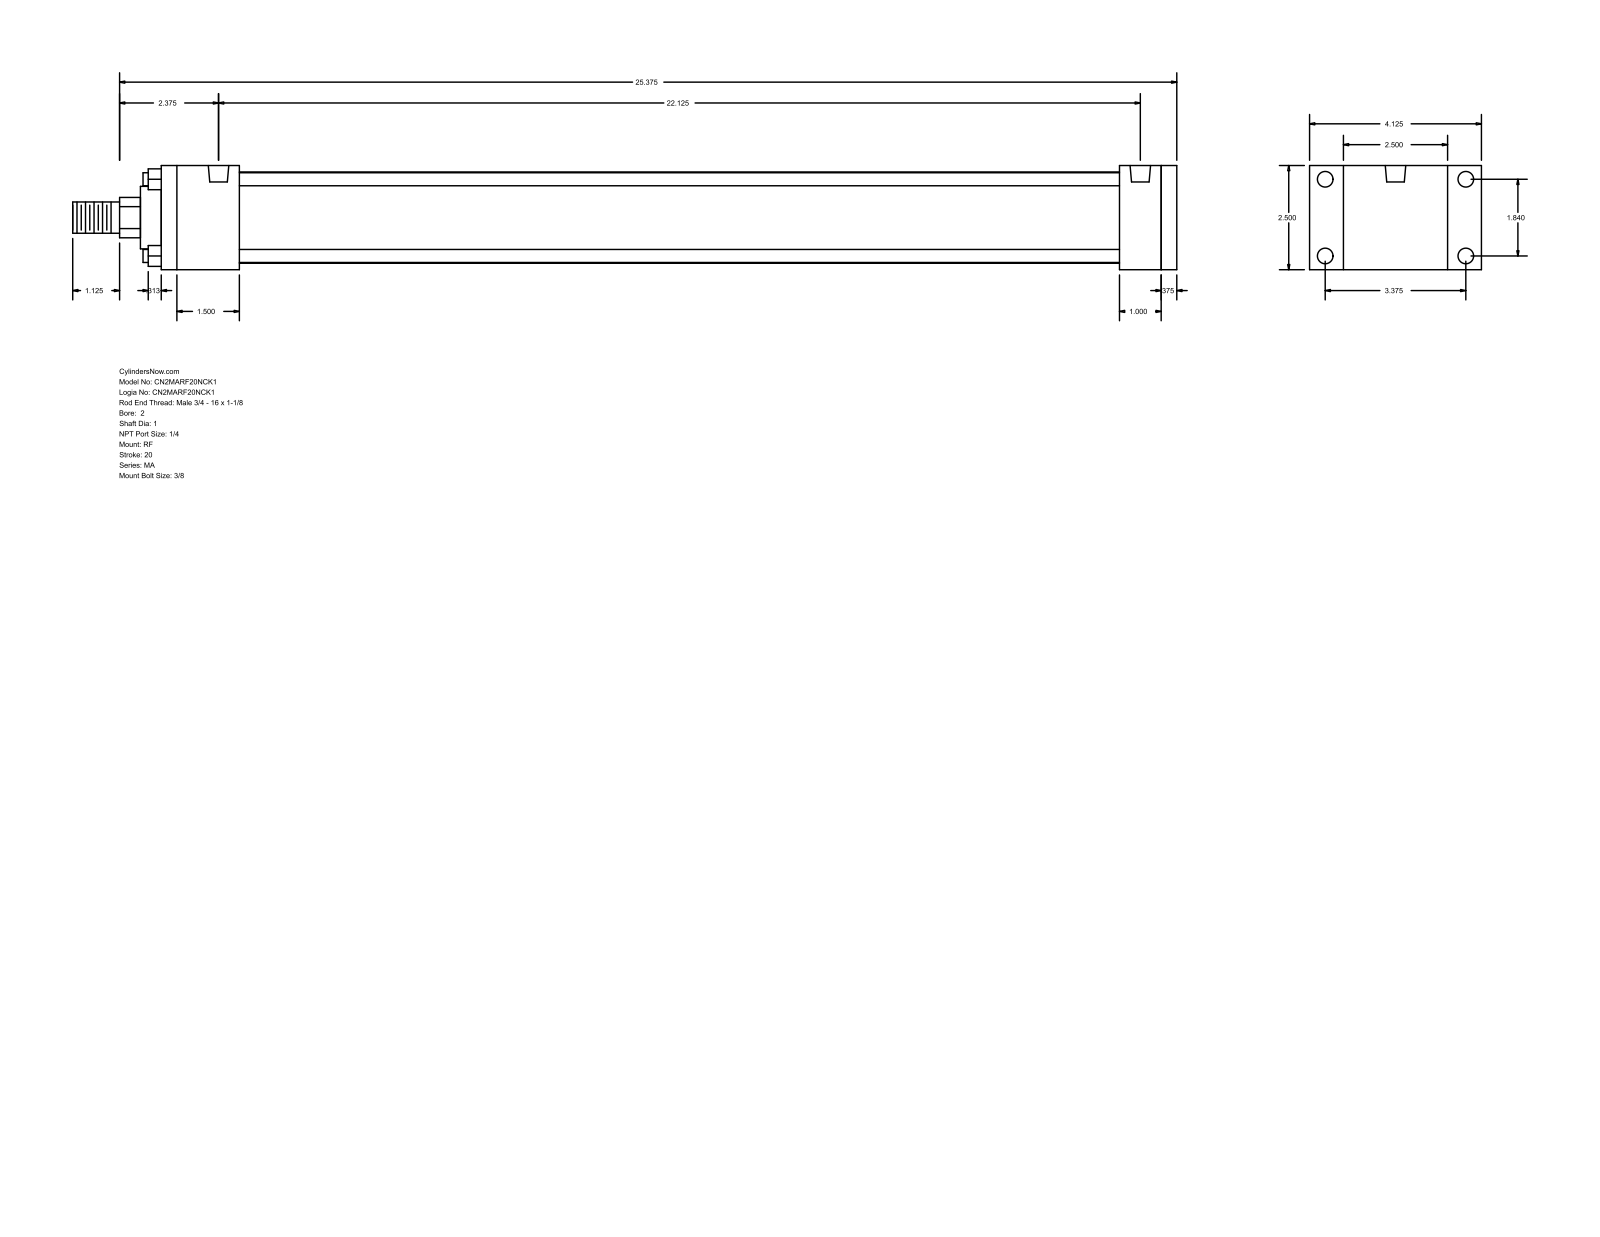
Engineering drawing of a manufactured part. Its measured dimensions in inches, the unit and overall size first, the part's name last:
Units: inches
Overall size (bounding box): 26.5 × 4.125 × 2.5
Round holes (diameter × count): ⌀0.313 ×4, ⌀0.375 ×4, ⌀0.492 ×2
Round bosses / shafts (diameter × count): ⌀0.313 ×4, ⌀2.19 ×1, ⌀1.5 ×1, ⌀1 ×1, ⌀0.75 ×1
Partial cylindrical surfaces — rounded edges, fillets, slot ends (radius × count): R0.484 ×1
Main face-to-face distances: 2.5, 24, 0.375, 24.375, 1, 0.813, 0.5, 1.875, 22.125, 22.5
Hole centre spacings: 1.84, 3.375, 3.844, 22.125
Bodies: 0 solids, 92 faces (64 planar, 28 cylindrical, 0 other)
Part name (STEP PRODUCT): MA_RF__0200_1
STEP written by: GSSL Pune (CONFIG_CONTROL_DESIGN)
